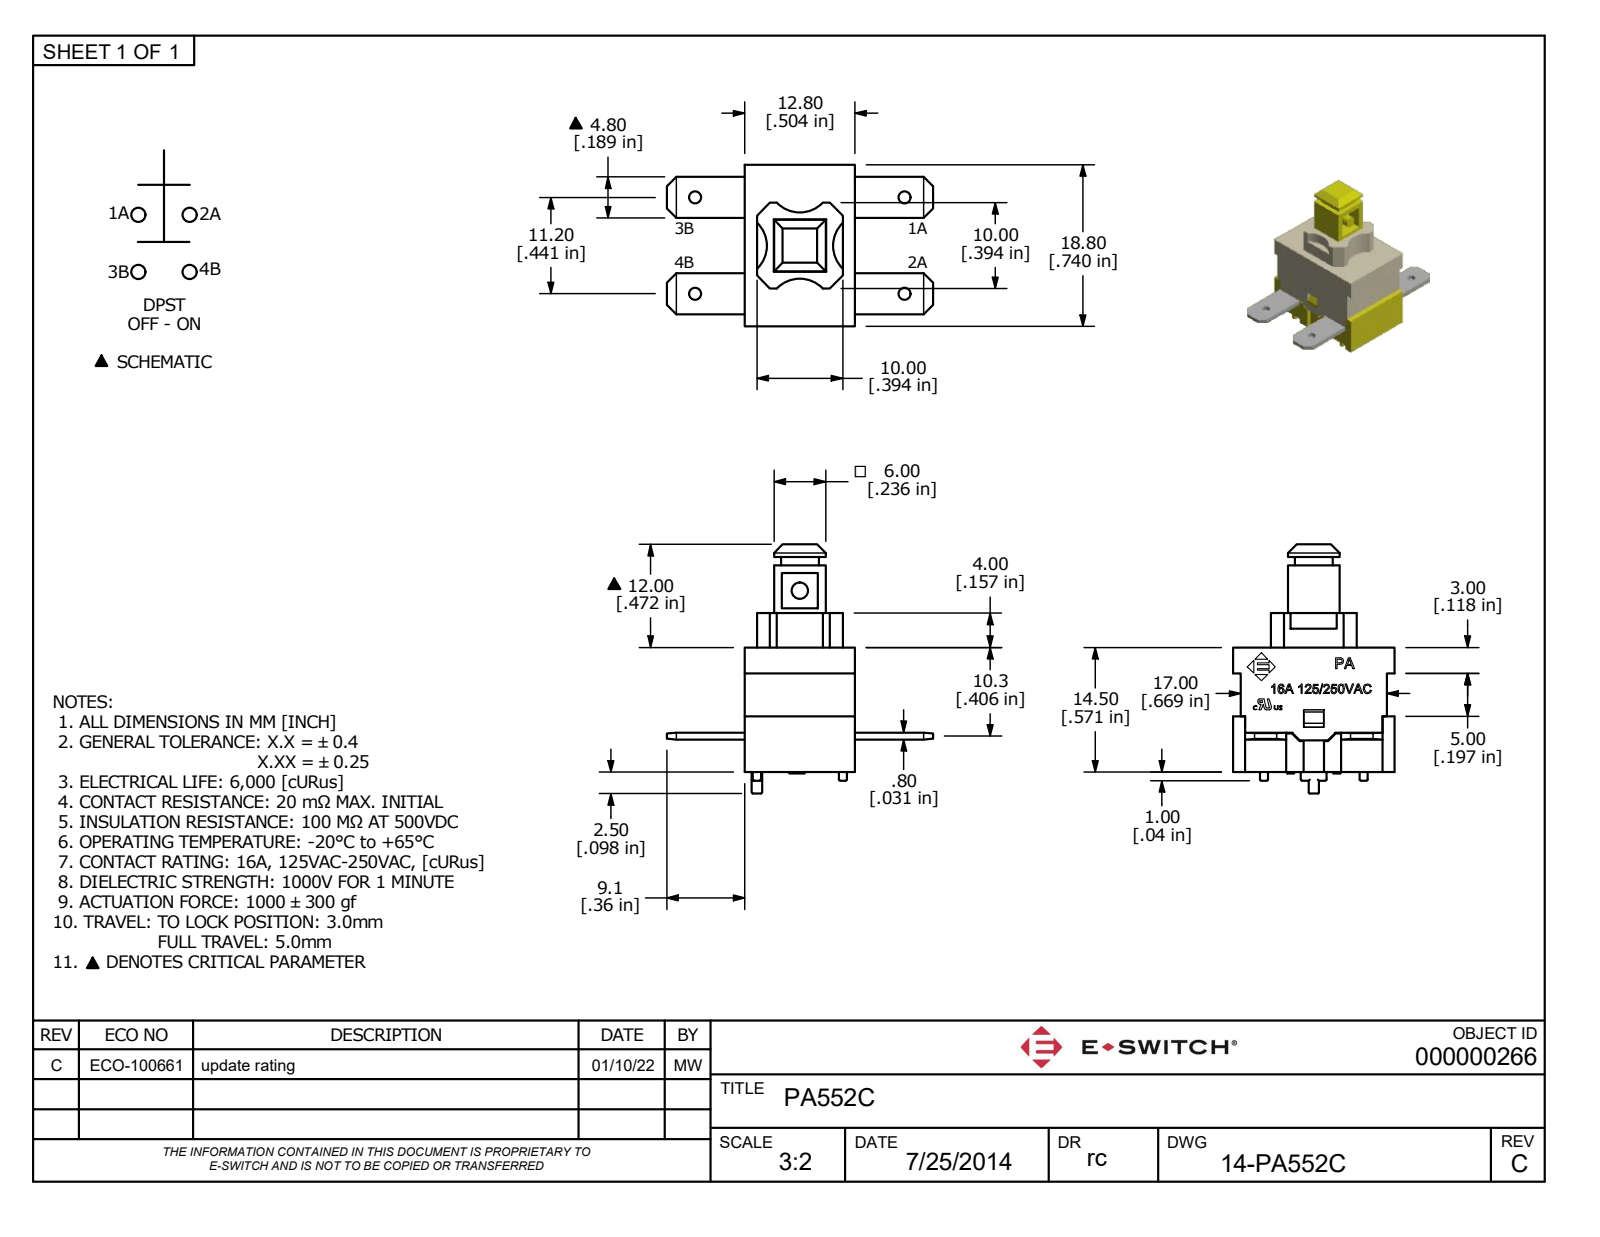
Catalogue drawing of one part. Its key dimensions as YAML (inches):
part_name: "PA552C"
step_written_by: "Autodesk Inventor 2022 (AUTOMOTIVE_DESIGN)"
units: inches
bodies: {solids: 1, faces: 830, planar: 619, cylindrical: 80, other: 131}
overall_size: [1.22, 1.142, 0.74]
volume: 0.137
surface_area: 7.13
round_holes:
  - {diameter: 0.055, count: 4}
  - {diameter: 0.118, count: 1}
round_bosses_or_shafts:
  - {diameter: 0.037, count: 4}
  - {diameter: 0.098, count: 2}
  - {diameter: 0.075, count: 1}
partial_cylinders:
  - {radius: 0.01, count: 22}
  - {radius: 0.005, count: 16}
  - {radius: 0.006, count: 8}
  - {radius: 0.146, count: 4}
  - {radius: 0.039, count: 2}
  - {radius: 0.02, count: 1}
  - {radius: 0.07, count: 1}
  - {radius: 0.091, count: 1}
face_to_face_distances: [0.031, 0.472, 0.035, 0.661, 0.079, 0.15, 0.441, 0.435, 0.339, 0.173]
hole_center_spacings: [0.528, 0.441, 0.961, 1.057]
